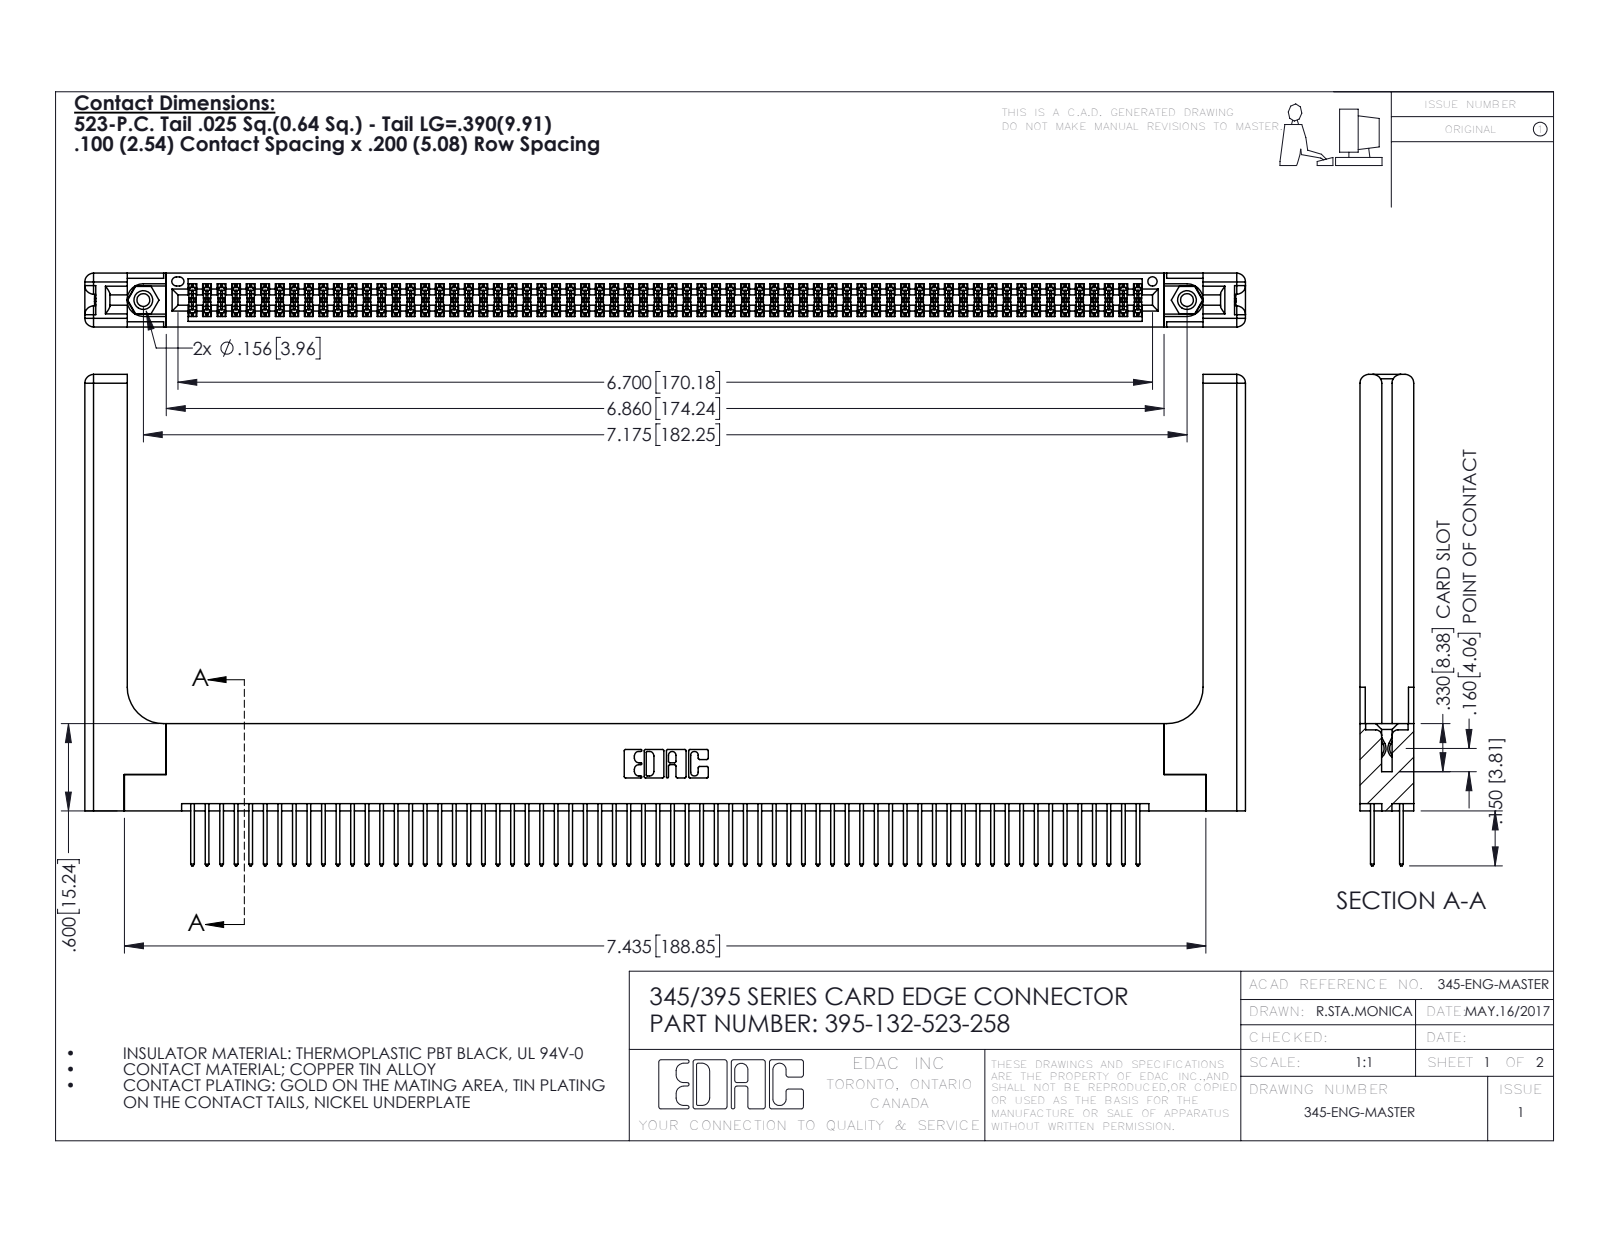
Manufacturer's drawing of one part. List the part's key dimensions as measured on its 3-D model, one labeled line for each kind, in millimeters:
Part name (STEP PRODUCT): 395-132-523-258; 345-250-001_345-250-001-102; 345 Part_Flush Mounting Lugs - 0.156 Dia-TH; 345-292-001_345-293-123 (+1 more)
STEP written by: SolidWorks 2016 (CONFIG_CONTROL_DESIGN)
Units: millimetres
Bodies: 137 solids, 6982 faces (4584 planar, 2338 cylindrical, 60 other)
Overall size (bounding box): 202.7 × 85.8 × 9.4
Volume: 28 660 mm³ · Surface area: 36 570 mm²
Round holes (diameter × count): ⌀2.3 ×2, ⌀3.2 ×2, ⌀4 ×2, ⌀1.6 ×1
Round bosses / shafts (diameter × count): ⌀3.9 ×2
Partial cylindrical surfaces — rounded edges, fillets, slot ends (radius × count): R0.2 ×198, R0.3 ×132, R0.3 ×22, R1.5 ×16, R0.2 ×6, R0.8 ×6, R0.7 ×3, R0.4 ×2
Main face-to-face distances: 1.8, 7.6, 9.4, 5.1, 2.5, 6.9, 0.6, 5.7, 4.4, 3.8
Hole centre spacings: 6.9, 176.3, 182.2
